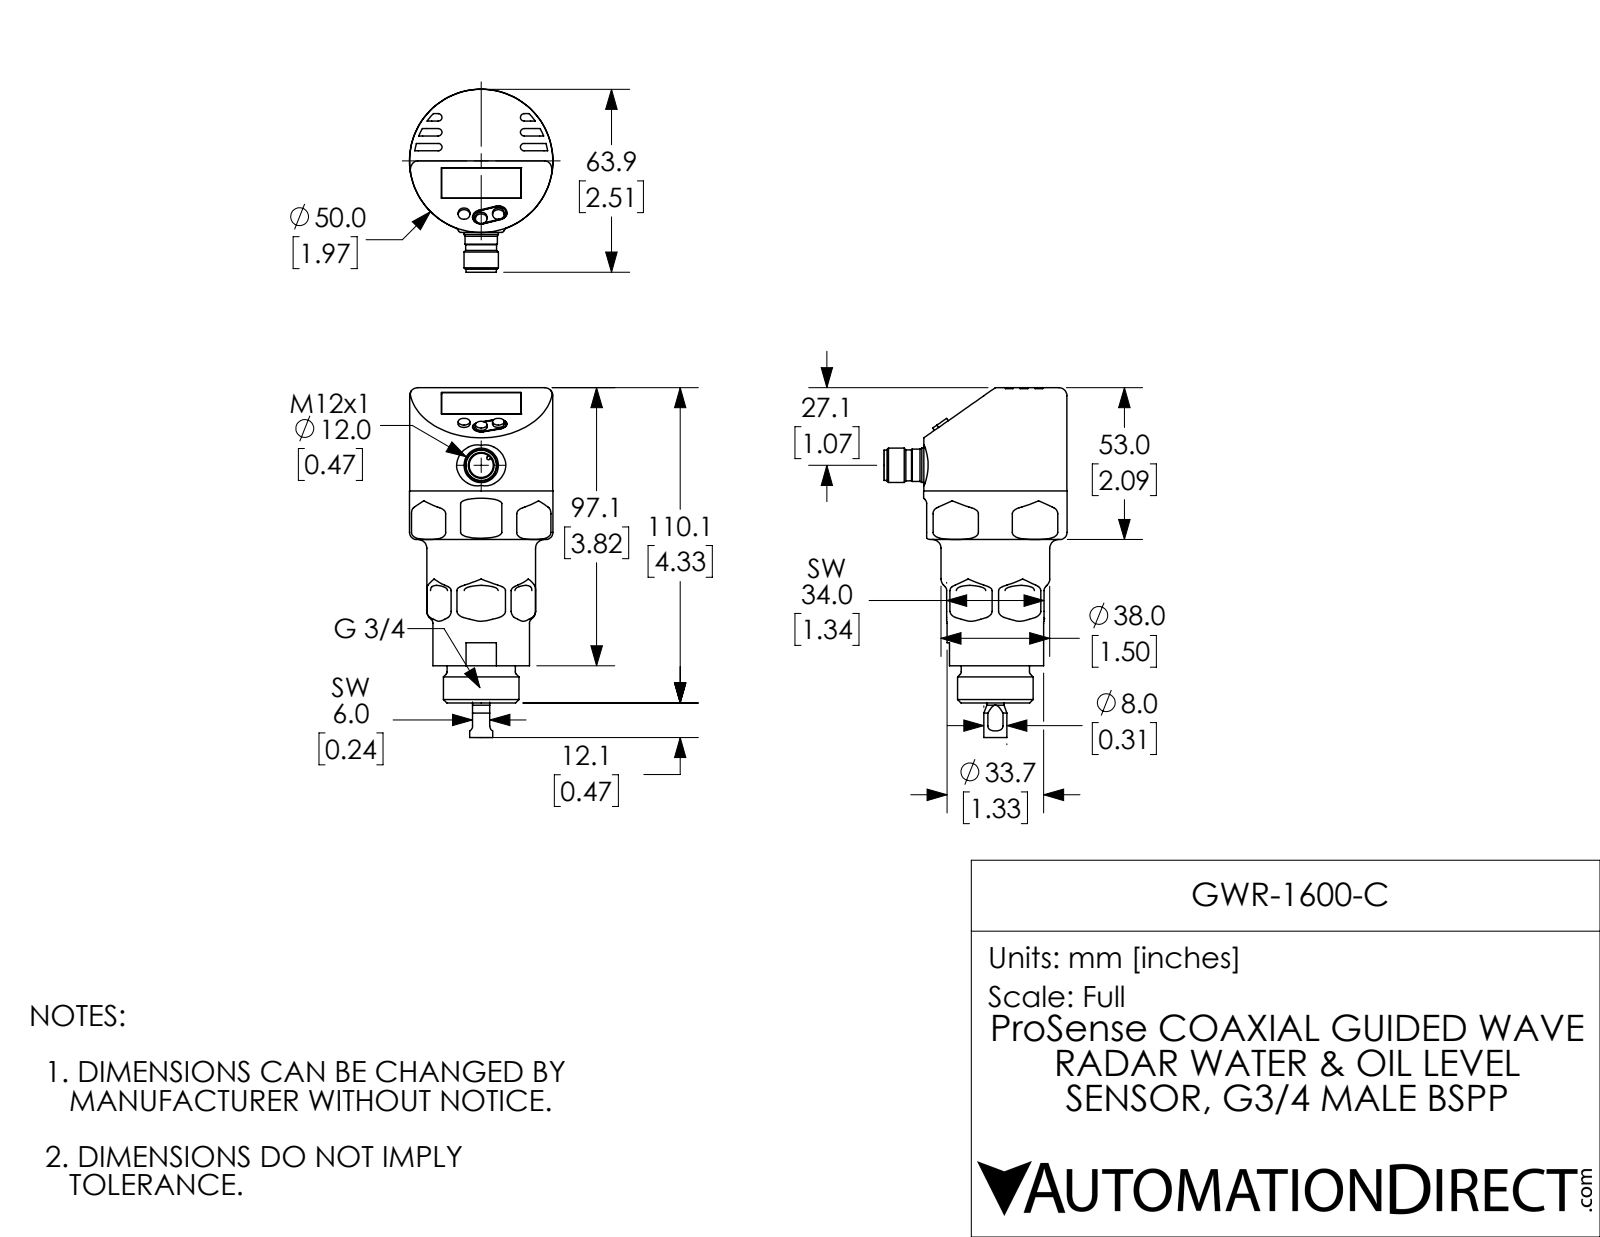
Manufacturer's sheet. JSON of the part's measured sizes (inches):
{"part_name": "GWR-1600-C", "step_written_by": "SolidWorks 2017 (AUTOMOTIVE_DESIGN)", "units": "inches", "bodies": {"solids": 1, "faces": 227, "planar": 85, "cylindrical": 91, "other": 51}, "overall_size": [4.807, 2.516, 1.972], "volume_in3": 9.026, "surface_area_in2": 28.91, "round_holes": [[0.333, 1], [1.154, 1]], "round_bosses_or_shafts": [[0.161, 3], [1.972, 1], [1.969, 1], [1.496, 1], [1.327, 1], [1.041, 1], [0.937, 1], [0.472, 1]], "partial_cylinders_radius": [[0.118, 16], [0.079, 9], [0.051, 6], [0.106, 2], [0.024, 1], [0.709, 1]], "face_to_face_distances": [1.339, 4.333, 1.812, 0.512, 3.821, 0.039, 0.047, 1.614, 0.276, 0.559]}
